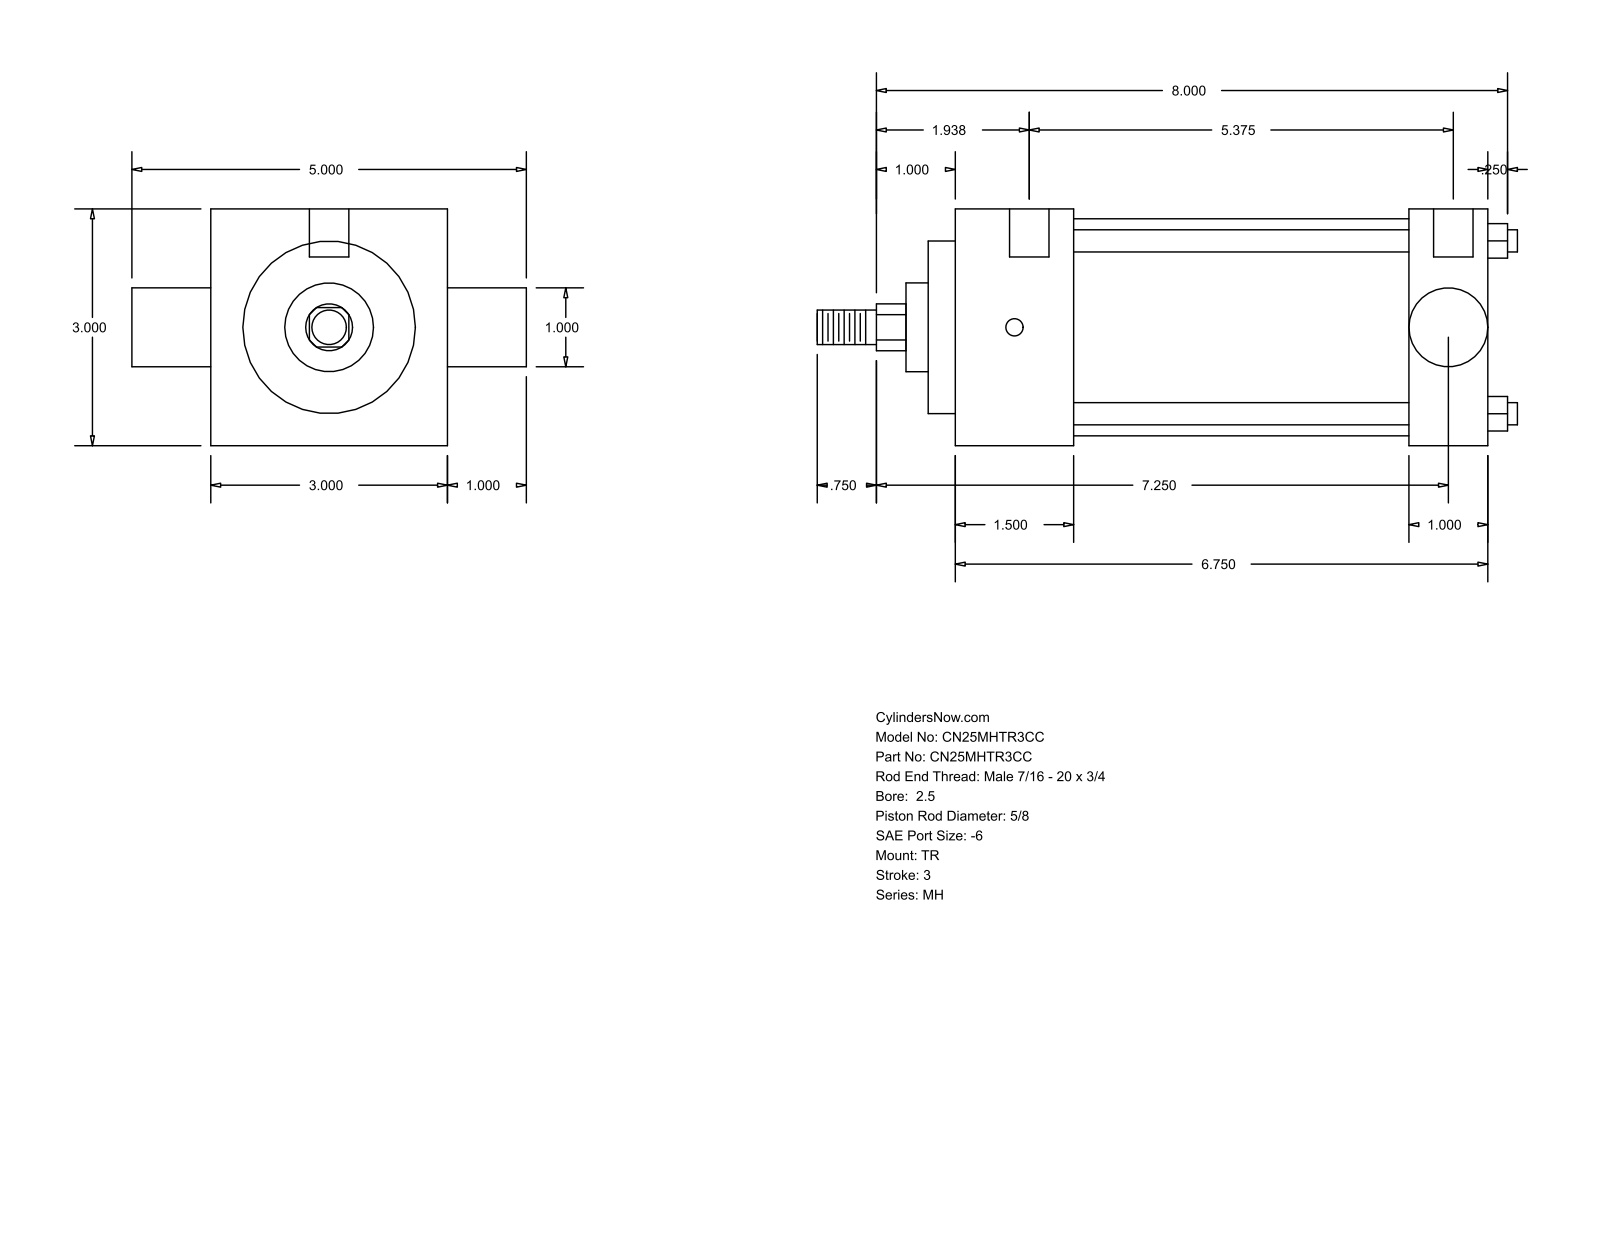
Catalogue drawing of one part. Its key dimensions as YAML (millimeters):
part_name: "MH_TR__0250_0.625"
step_written_by: "GSSL Pune (CONFIG_CONTROL_DESIGN)"
units: millimeters
bodies: {solids: 0, faces: 86, planar: 61, cylindrical: 25, other: 0}
overall_size: [225.43, 127, 76.2]
round_holes:
  - {diameter: 5.56, count: 3}
  - {diameter: 12.7, count: 2}
round_bosses_or_shafts:
  - {diameter: 7.14, count: 4}
  - {diameter: 69.85, count: 1}
  - {diameter: 55.55, count: 1}
  - {diameter: 28.57, count: 1}
  - {diameter: 25.35, count: 1}
  - {diameter: 15.88, count: 1}
  - {diameter: 11.11, count: 1}
partial_cylinders:
  - {radius: 7.54, count: 1}
face_to_face_distances: [76.2, 171.45, 25.4, 38.1, 133.35, 146.05, 107.95, 8.73, 46.83, 154.78]
hole_center_spacings: [3.17, 4.76, 136.53, 139.7, 141.29, 144.46]
